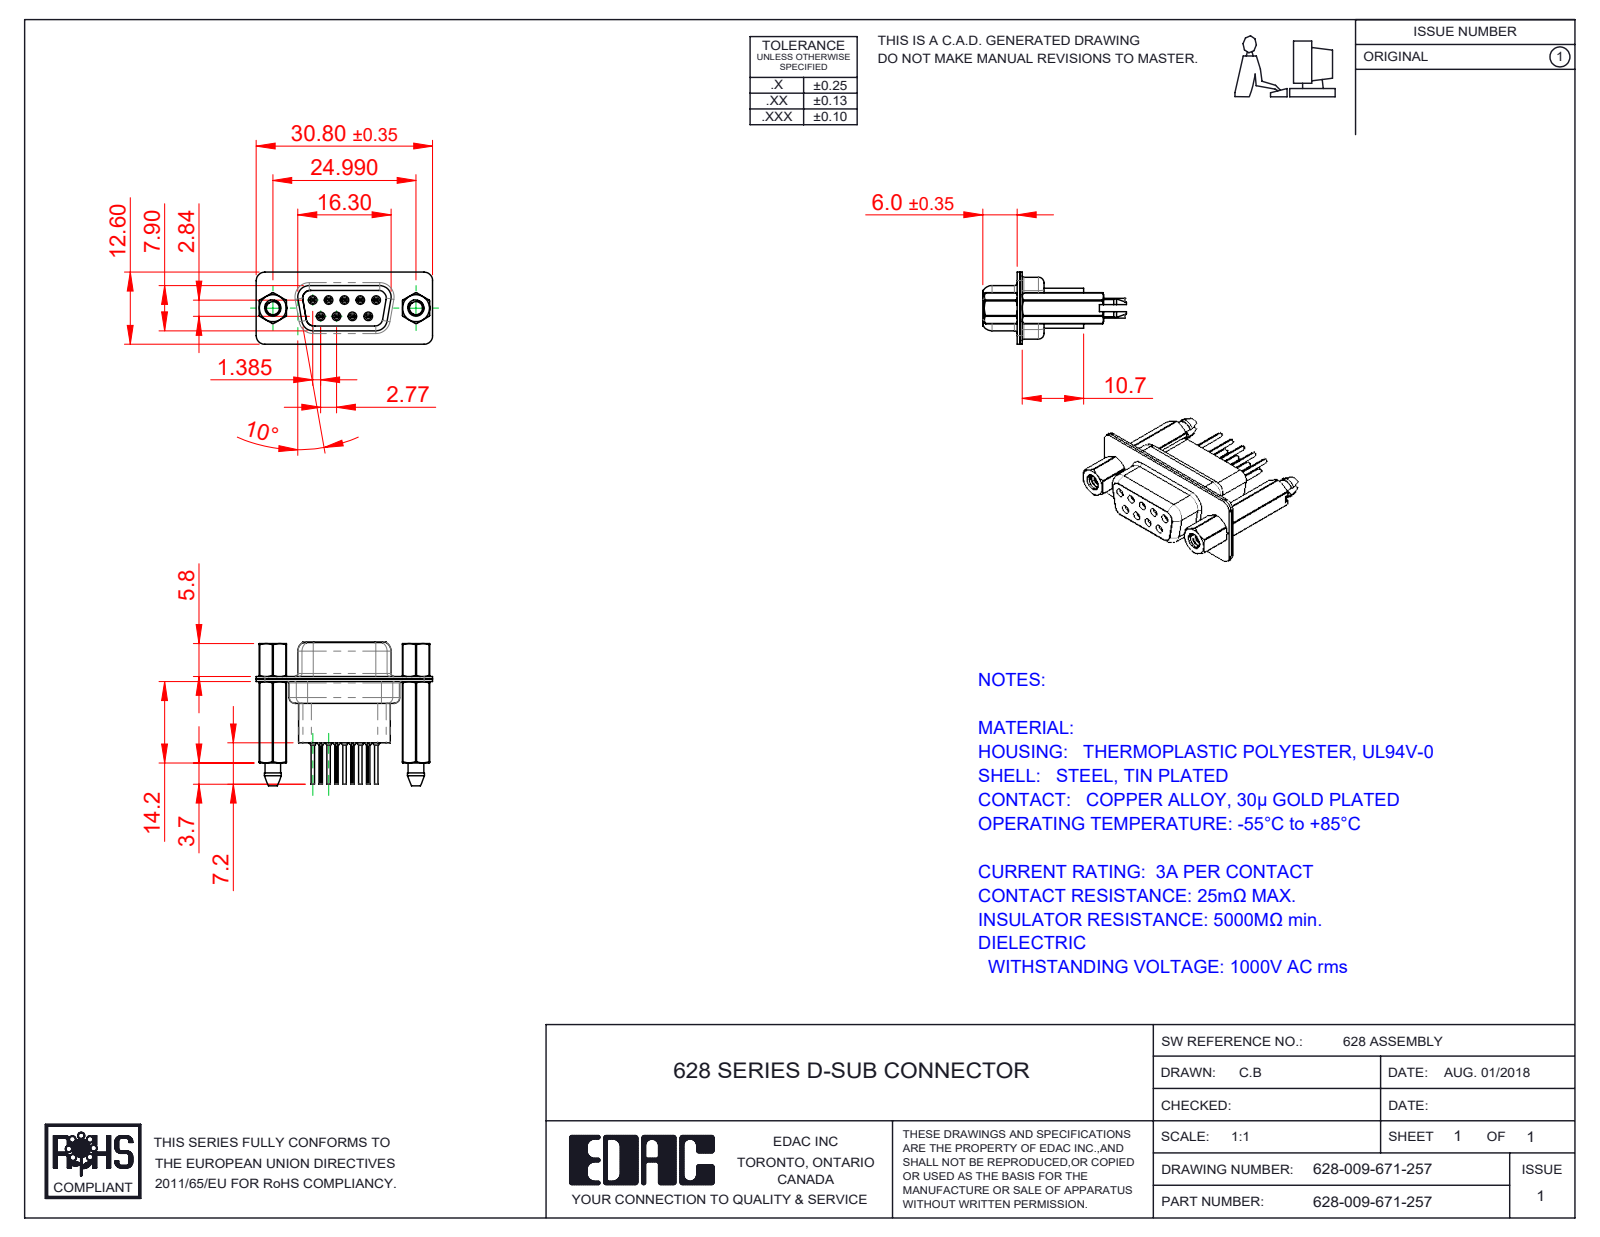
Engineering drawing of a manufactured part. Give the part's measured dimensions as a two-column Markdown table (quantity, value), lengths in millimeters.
| quantity | value |
| --- | --- |
| part name | 628 Contact Row 1_71; 628 Shell Front_09 Contacts; 628 4-40 Threaded Boardlock_HP71; 628 Contact Row 2_71 (+4 more) |
| STEP written by | SolidWorks 2020 (CONFIG_CONTROL_DESIGN) |
| units | millimeters |
| bodies | 16 solids, 1586 faces (400 planar, 538 cylindrical, 648 other) |
| overall size | 30.8 × 25.1 × 12.6 |
| volume | 2 822 mm³ |
| surface area | 6 568 mm² |
| round holes (diameter × count) | 0.2 × 9, 0.8 × 9, 0.9 × 9, 1.1 × 9, 1.6 × 9, 1.7 × 5, 2.26 × 2, 2.29 × 2, 4 × 2, 4.05 × 2, 4.85 × 2 |
| round bosses / shafts (diameter × count) | 2 × 9, 1.5 × 9, 1.2 × 9, 0.6 × 9, 4.95 × 2, 4.8 × 2, 2.79 × 2 |
| partial cylindrical surfaces (radius × count) | 1.5 × 19, 0.1 × 18, 2 × 12, 0.28 × 9, 1.35 × 6, 1.6 × 6, 0.25 × 4, 0.5 × 4 |
| main face-to-face distances | 0.45, 0.4, 0.9, 4.76, 8.5, 6.6, 1.9, 1.4, 7, 0.5 |
| hole center spacings | 3.16, 2.77, 5.54, 5.03, 5.04, 8.31, 7.48, 7.49 |
